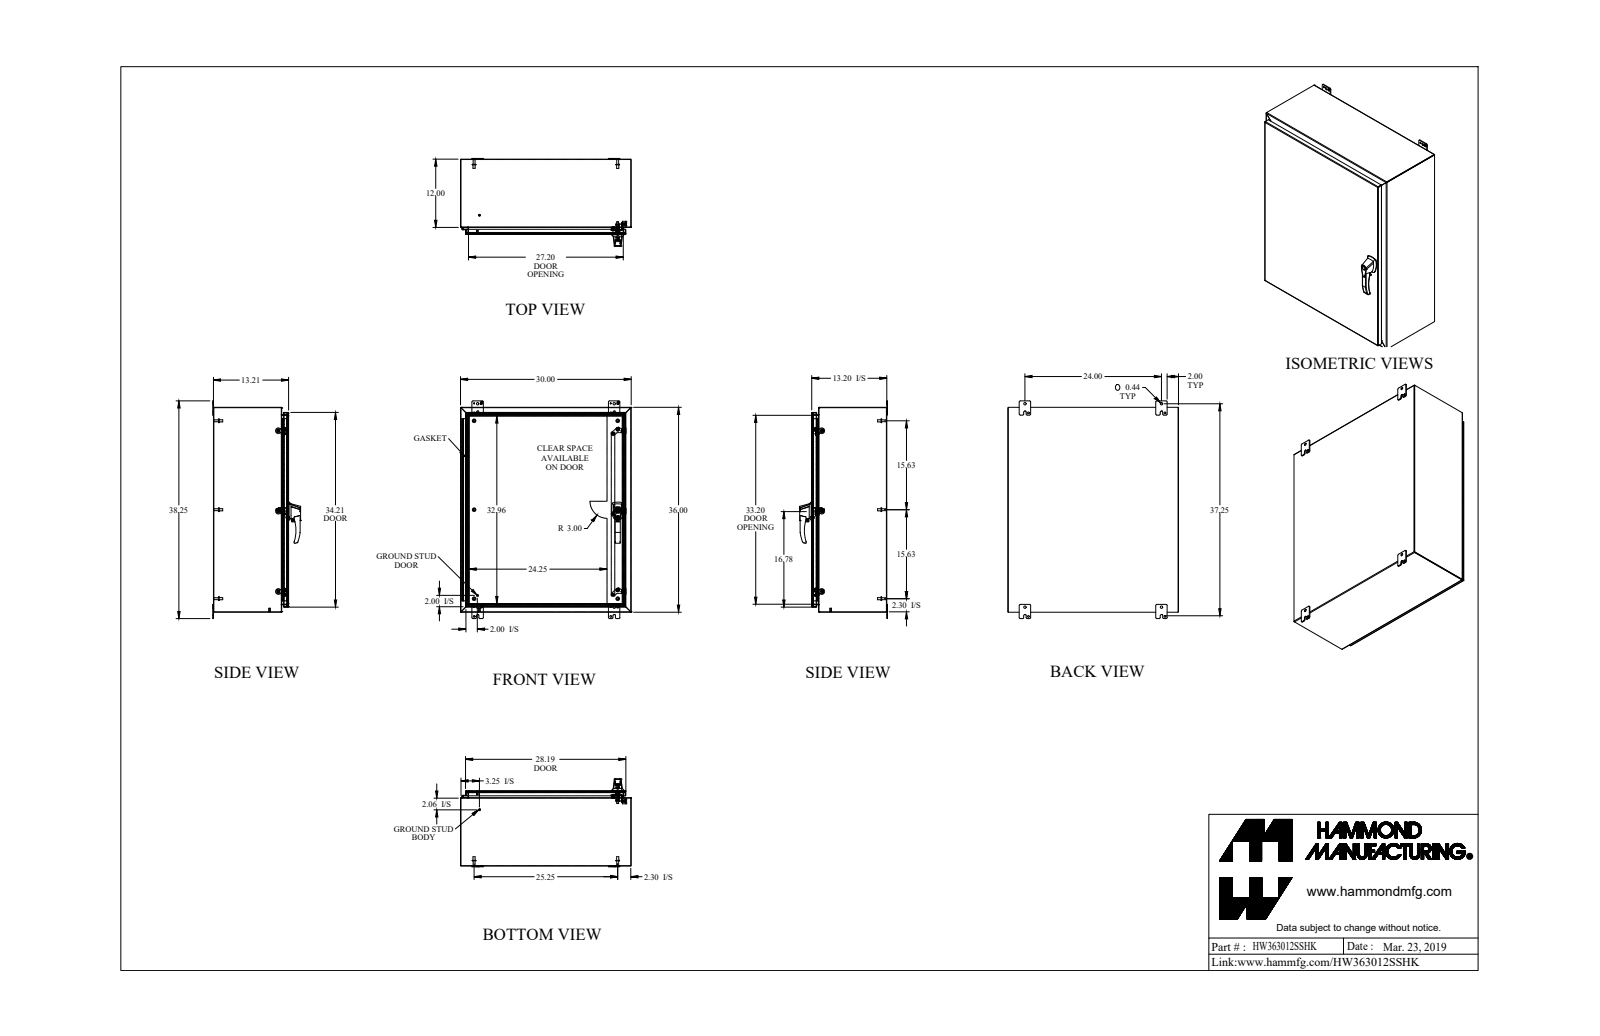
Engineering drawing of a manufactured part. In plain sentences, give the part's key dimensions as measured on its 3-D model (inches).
The part is named "HW363012SSHK". Its 3-D file was written by "SolidWorks 2018 (AUTOMOTIVE_DESIGN)". It is 46 solids with 1508 faces: 721 planar, 629 cylindrical and 158 other. Overall it measures 38.25 by 30 by 15.45 inches. Its volume is 331.6 cubic inches and its surface area 8 790 square inches. Round holes: 6 of diameter 0.176, 5 of diameter 0.313, 3 of diameter 0.25, 3 of diameter 0.265, 3 of diameter 0.413, 2 of diameter 0.196, 2 of diameter 0.256, 2 of diameter 0.394, 2 of diameter 0.437, 1 of diameter 0.187, 1 of diameter 0.233, 1 of diameter 0.33. Round bosses or shafts: 11 of diameter 0.375, 7 of diameter 0.25, 6 of diameter 0.65, 6 of diameter 0.332, 6 of diameter 0.156, 3 of diameter 1, 3 of diameter 0.51, 2 of diameter 0.63. Partial cylindrical surfaces (rounded edges, fillets, slot ends): 27 of radius 0.25, 24 of radius 0.188, 18 of radius 0.036, 18 of radius 0.108, 12 of radius 0.06, 9 of radius 0.125, 8 of radius 0.045, 8 of radius 0.218. The main face-to-face distances are 0.072, 13.138, 13.066, 0.072, 13.138, 13.21, 29.928, 35.928, 29.856, 30. The hole center spacings are 14.118, 14.119, 28.237, 1.11, 1.111, 14.119, 24, 24.724.
